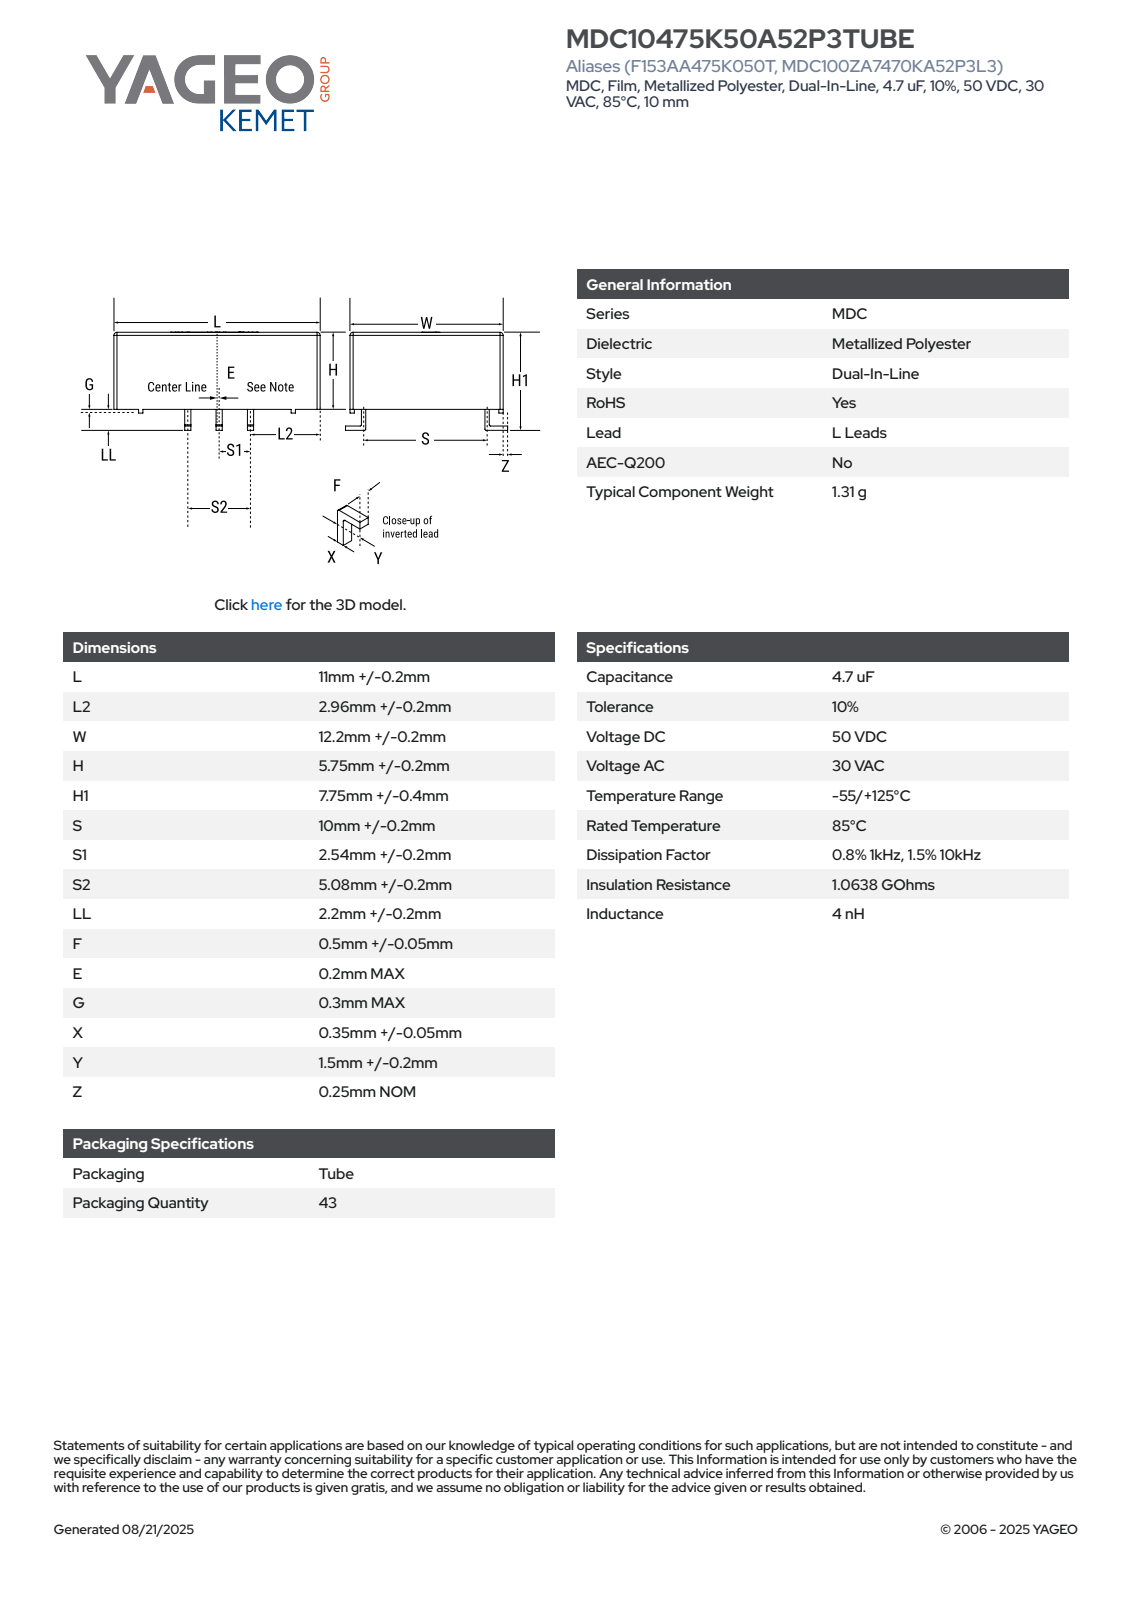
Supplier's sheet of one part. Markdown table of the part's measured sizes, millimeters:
| quantity | value |
| --- | --- |
| part name | CFS_KD6MDC_A52_L11.2L23.16W12.4H5.95S10LL2.4 |
| STEP written by | SolidWorks 2021 (AUTOMOTIVE_DESIGN) |
| units | millimeters |
| bodies | 4 solids, 117 faces (113 planar, 0 cylindrical, 4 other) |
| overall size | 13.2 × 11.2 × 8.36 |
| volume | 826 mm³ |
| surface area | 598 mm² |
| main face-to-face distances | 5.95, 11.2, 12.4, 0.4, 1.3, 11.5, 11.1, 0.9, 10.2, 2.78 |
